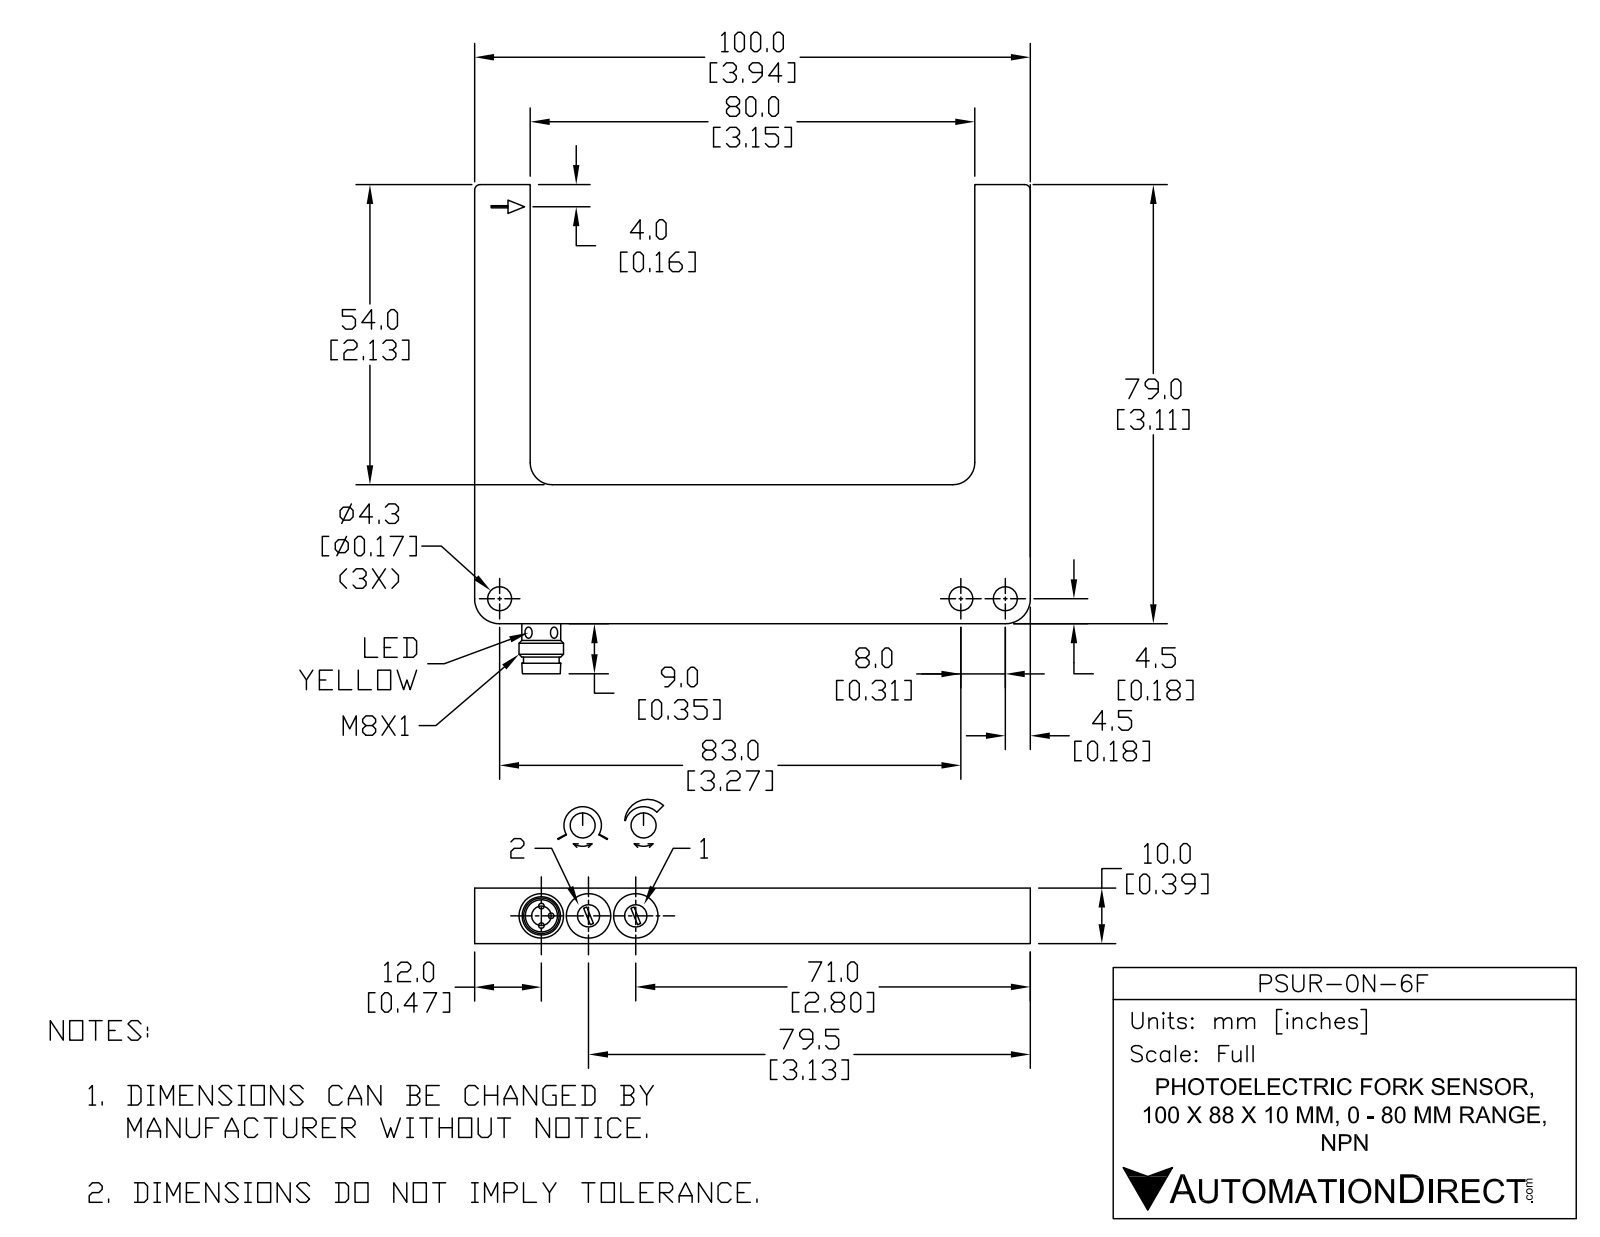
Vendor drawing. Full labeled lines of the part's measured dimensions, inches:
Part name (STEP PRODUCT): PSUR-0N-6F
STEP written by: SolidWorks 2019 (AUTOMOTIVE_DESIGN)
Units: inches
Bodies: 1 solid, 95 faces (35 planar, 48 cylindrical, 12 other)
Overall size (bounding box): 3.937 × 3.465 × 0.394
Volume: 2.17 in³ · Surface area: 19.25 in²
Round holes (diameter × count): ⌀0.169 ×3, ⌀0.079 ×2, ⌀0.157 ×2, ⌀0.315 ×2, ⌀0.228 ×1
Round bosses / shafts (diameter × count): ⌀0.039 ×3, ⌀0.315 ×1, ⌀0.267 ×1
Partial cylindrical surfaces — rounded edges, fillets, slot ends (radius × count): R0.02 ×2, R0.039 ×2, R0.063 ×2, R0.157 ×2, R0.177 ×2
Main face-to-face distances: 0.394, 3.543, 3.937, 0.984, 3.15, 2.126, 3.11, 3.106, 0.98, 0.157
Hole centre spacings: 0.335, 0.315, 0.669, 3.268, 3.583
